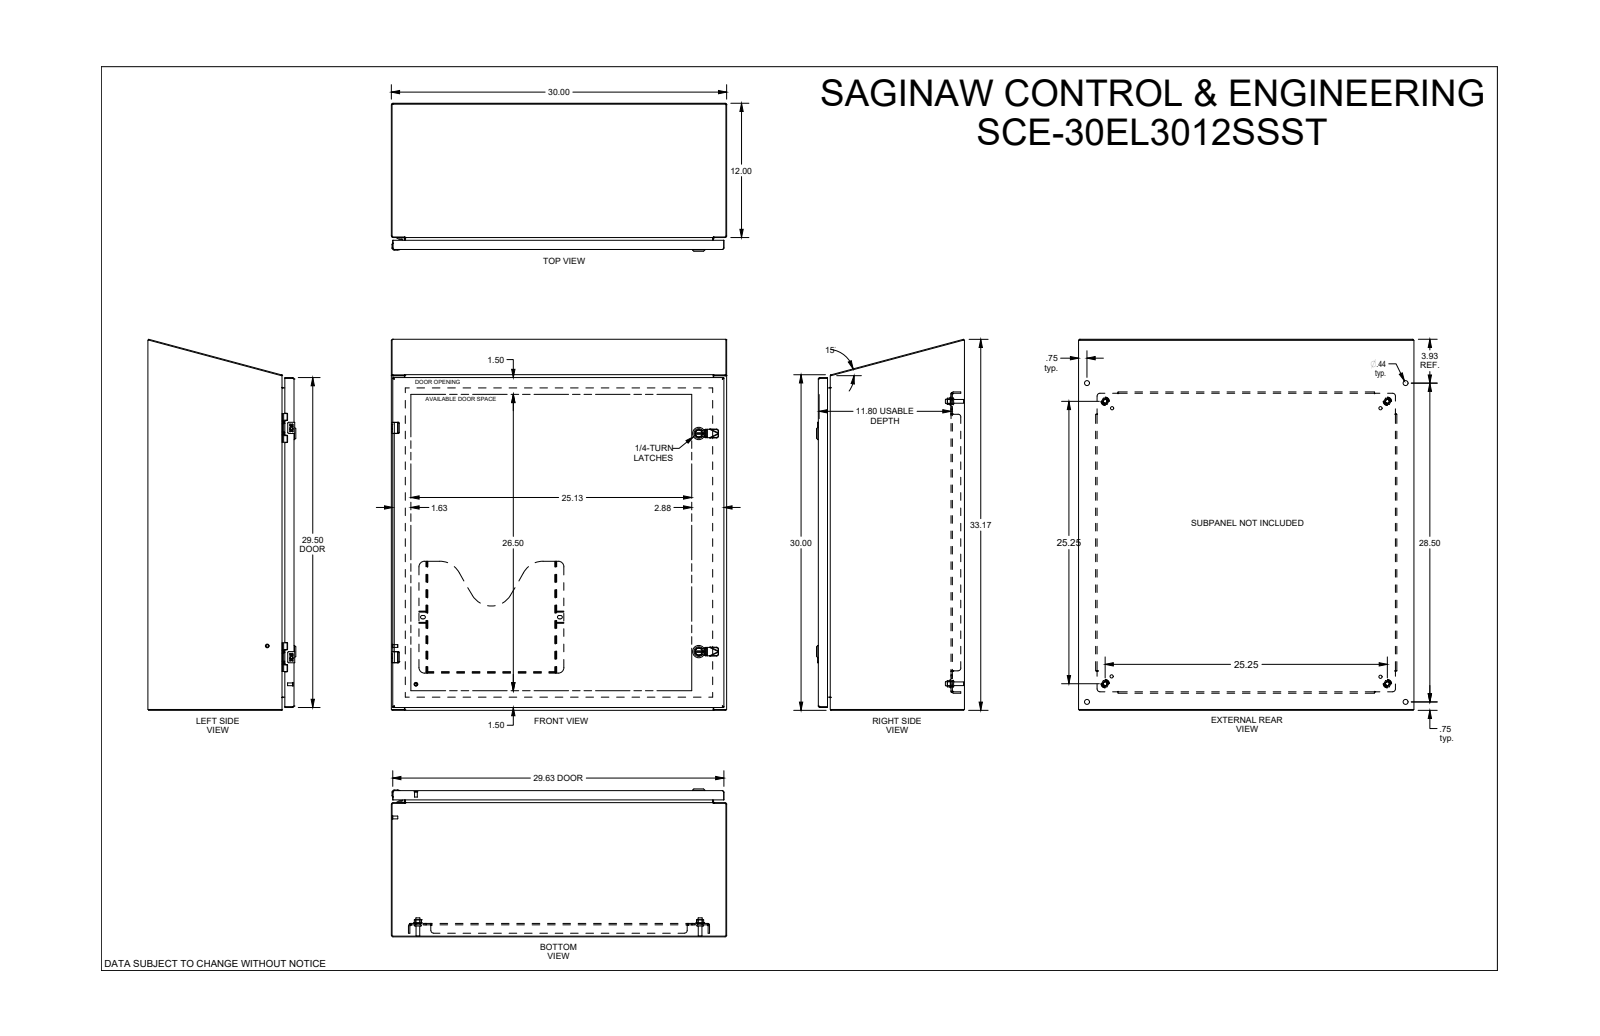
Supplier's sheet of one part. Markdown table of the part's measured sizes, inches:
| quantity | value |
| --- | --- |
| part name | SCE-30EL3012SSST |
| STEP written by | SolidWorks 2019 (CONFIG_CONTROL_DESIGN) |
| units | inches |
| bodies | 0 solids, 2844 faces (1311 planar, 759 cylindrical, 774 other) |
| overall size | 33.178 × 30 × 13.23 |
| round holes (diameter × count) | 0.172 × 4, 0.205 × 4, 0.244 × 4, 0.266 × 4, 0.281 × 4, 0.367 × 4, 0.375 × 4, 0.437 × 4, 0.5 × 4, 0.156 × 2, 0.197 × 2, 0.218 × 2 |
| round bosses / shafts (diameter × count) | 0.17 × 6, 0.366 × 4, 0.332 × 4, 0.25 × 4, 0.248 × 4, 0.196 × 3, 1.102 × 2, 0.866 × 2 |
| partial cylindrical surfaces (radius × count) | 0.012 × 56, 0.01 × 28, 0.015 × 28, 0.04 × 23, 0.02 × 20, 0.07 × 14, 0.029 × 12, 0.06 × 11 |
| main face-to-face distances | 0.075, 12.998, 12.923, 0.075, 13.073, 12.998, 1.2, 11.873, 0.125, 29.925 |
| hole center spacings | 0.985, 26.352, 26.924, 20.5, 24.639, 0.02, 0.875, 4.493 |
